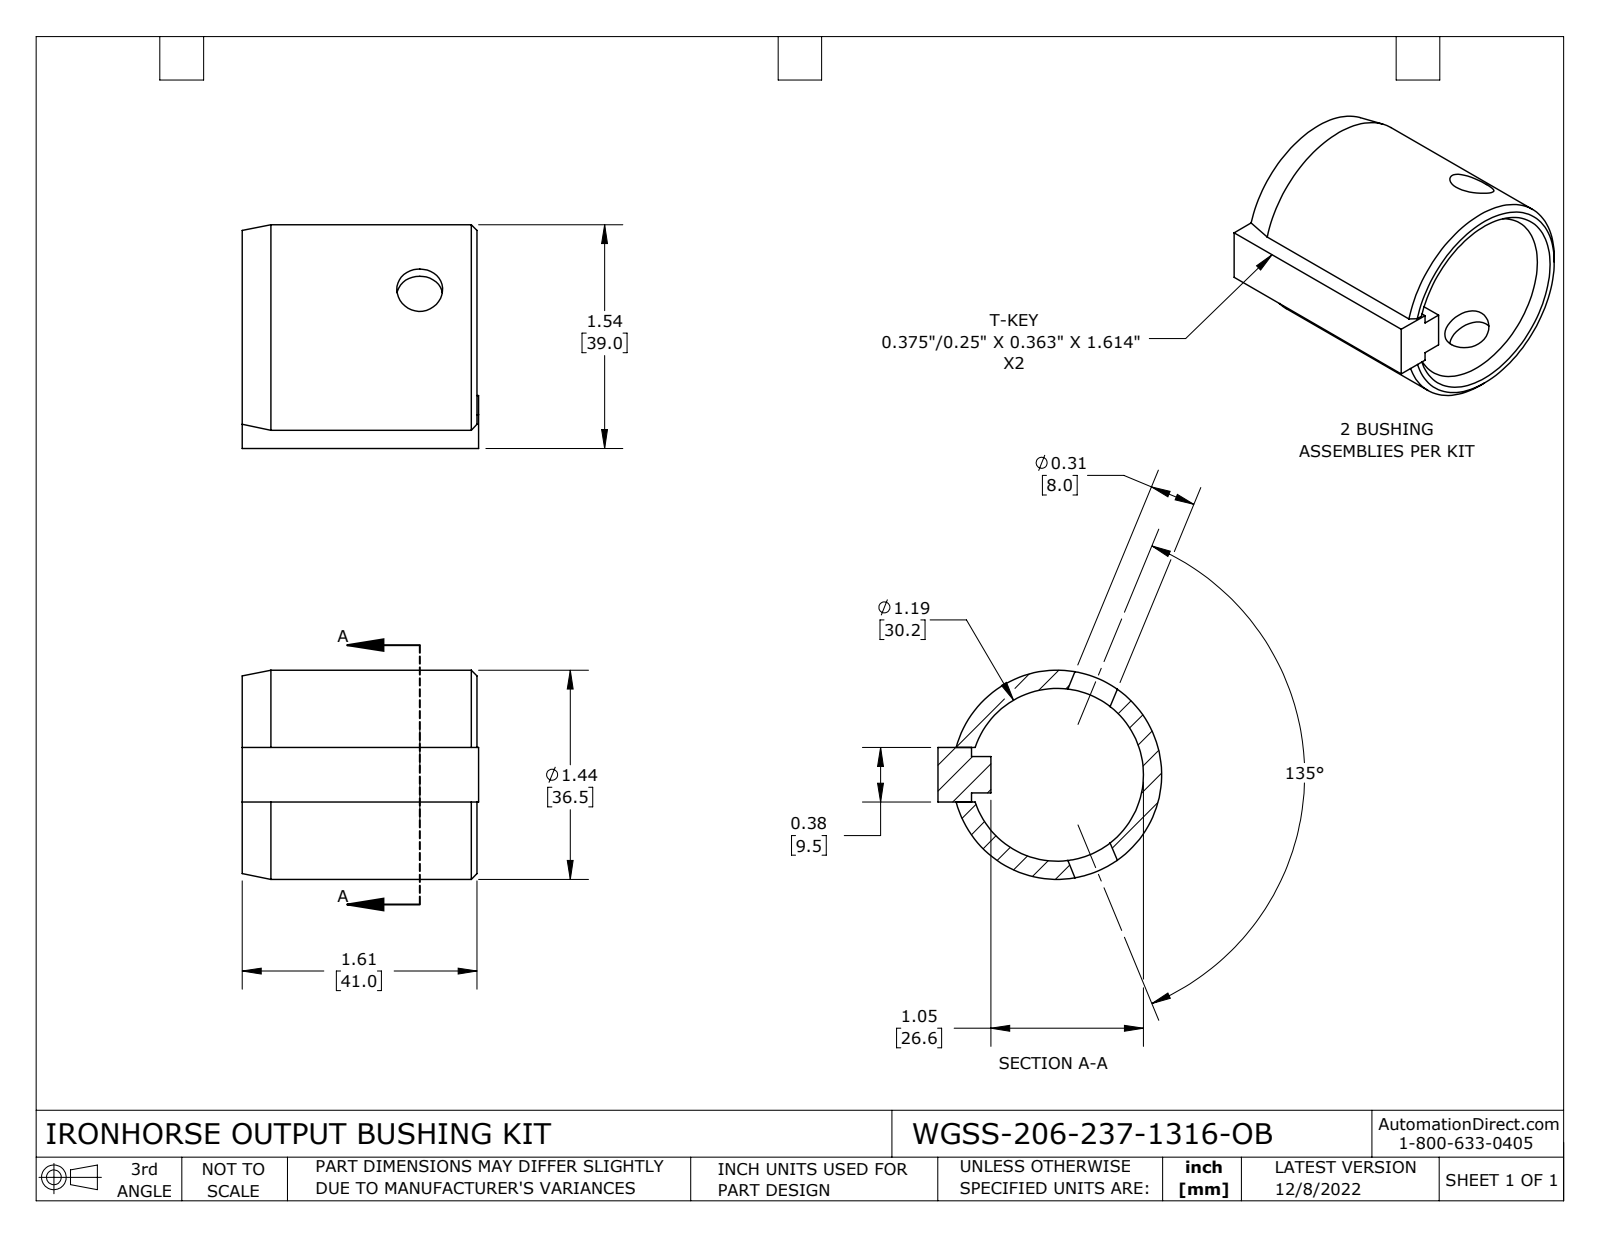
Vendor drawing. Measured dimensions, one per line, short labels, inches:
name: WGSS-206-237-1316-OB
written by: SolidWorks 2021 (CONFIG_CONTROL_DESIGN)
unit: in
bodies: 2 solids, 36 faces (14 planar, 10 cylindrical, 12 other)
size: 1.625 × 1.537 × 1.437
volume: 0.899 in³; area: 15.52 in²
holes: 2× ⌀0.315, 1× ⌀1.187
bosses: 1× ⌀1.437
face distances: 0.375, 0.363, 0.062, 0.312, 0.25, 0.313, 0.063, 0.133, 0.231, 1.614
